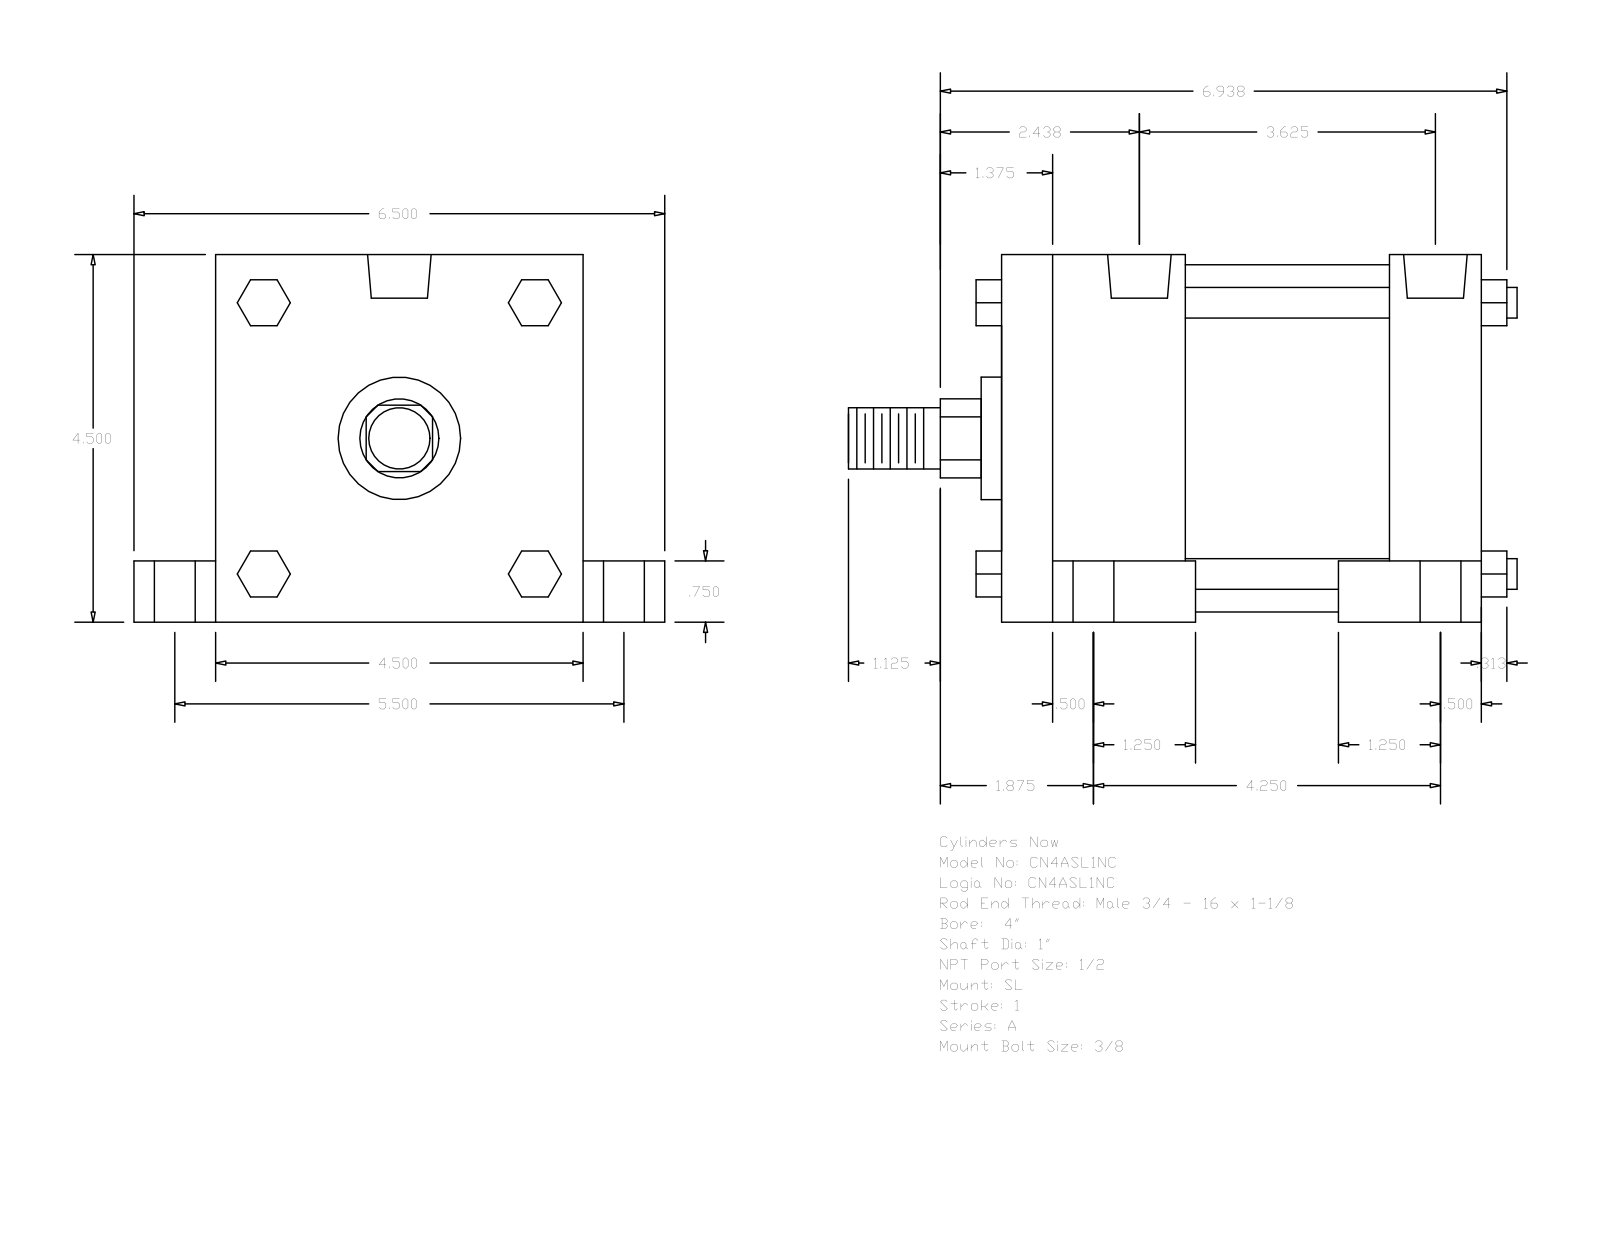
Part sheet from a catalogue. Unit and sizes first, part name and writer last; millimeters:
Units: millimetres
Overall size (bounding box): 207.96 × 165.1 × 114.3
Round holes (diameter × count): ⌀8.73 ×4, ⌀12.7 ×4, ⌀19.05 ×4, ⌀19.77 ×2
Round bosses / shafts (diameter × count): ⌀9.53 ×4, ⌀107.95 ×1, ⌀38.1 ×1, ⌀25.4 ×1, ⌀19.05 ×1
Partial cylindrical surfaces — rounded edges, fillets, slot ends (radius × count): R12.29 ×1
Main face-to-face distances: 114.3, 149.23, 63.5, 57.15, 92.08, 120.65, 28.58, 139.7, 19.05, 25.4
Hole centre spacings: 3.18, 69.87, 70.01, 71.3, 72, 85.72, 88.9, 107.95
Bodies: 0 solids, 150 faces (114 planar, 36 cylindrical, 0 other)
Part name (STEP PRODUCT): A_SL__0400_1
STEP written by: GSSL Pune (CONFIG_CONTROL_DESIGN)
